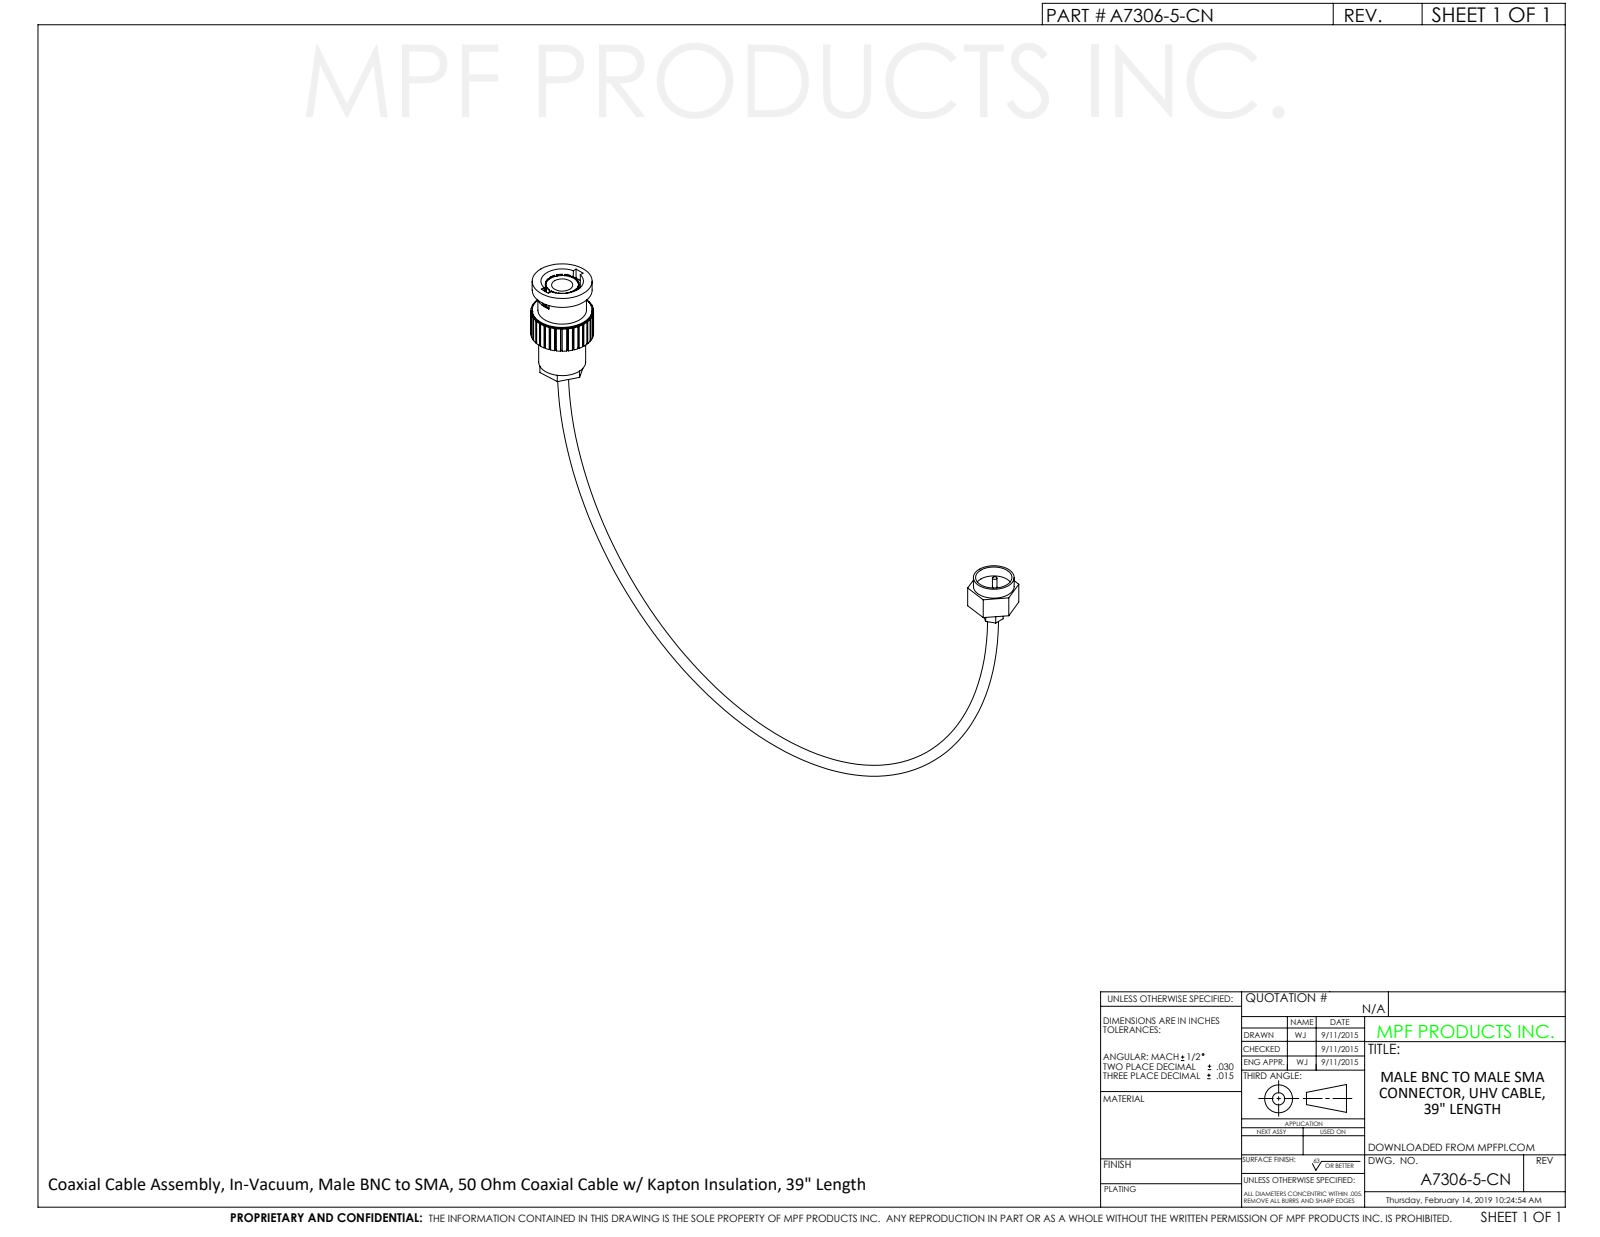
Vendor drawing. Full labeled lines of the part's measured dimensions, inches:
Part name (STEP PRODUCT): A7306-5-CN
STEP written by: SolidWorks 2012 (CONFIG_CONTROL_DESIGN)
Units: inches
Bodies: 2 solids, 331 faces (237 planar, 92 cylindrical, 2 other)
Overall size (bounding box): 6.109 × 3.816 × 0.575
Volume: 0.239 in³ · Surface area: 7.38 in²
Round holes (diameter × count): ⌀0.074 ×1, ⌀0.158 ×1, ⌀0.194 ×1, ⌀0.334 ×1, ⌀0.39 ×1
Round bosses / shafts (diameter × count): ⌀0.55 ×1, ⌀0.525 ×1, ⌀0.445 ×1, ⌀0.43 ×1, ⌀0.374 ×1, ⌀0.308 ×1, ⌀0.041 ×1
Partial cylindrical surfaces — rounded edges, fillets, slot ends (radius × count): R0.068 ×1, R0.15 ×1, R0.151 ×1, R0.287 ×1
Main face-to-face distances: 0.409, 0.15, 0.35, 0.2, 0.978, 0.828, 0.628, 0.1, 0.528, 0.54
Hole centre spacings: 5.595
